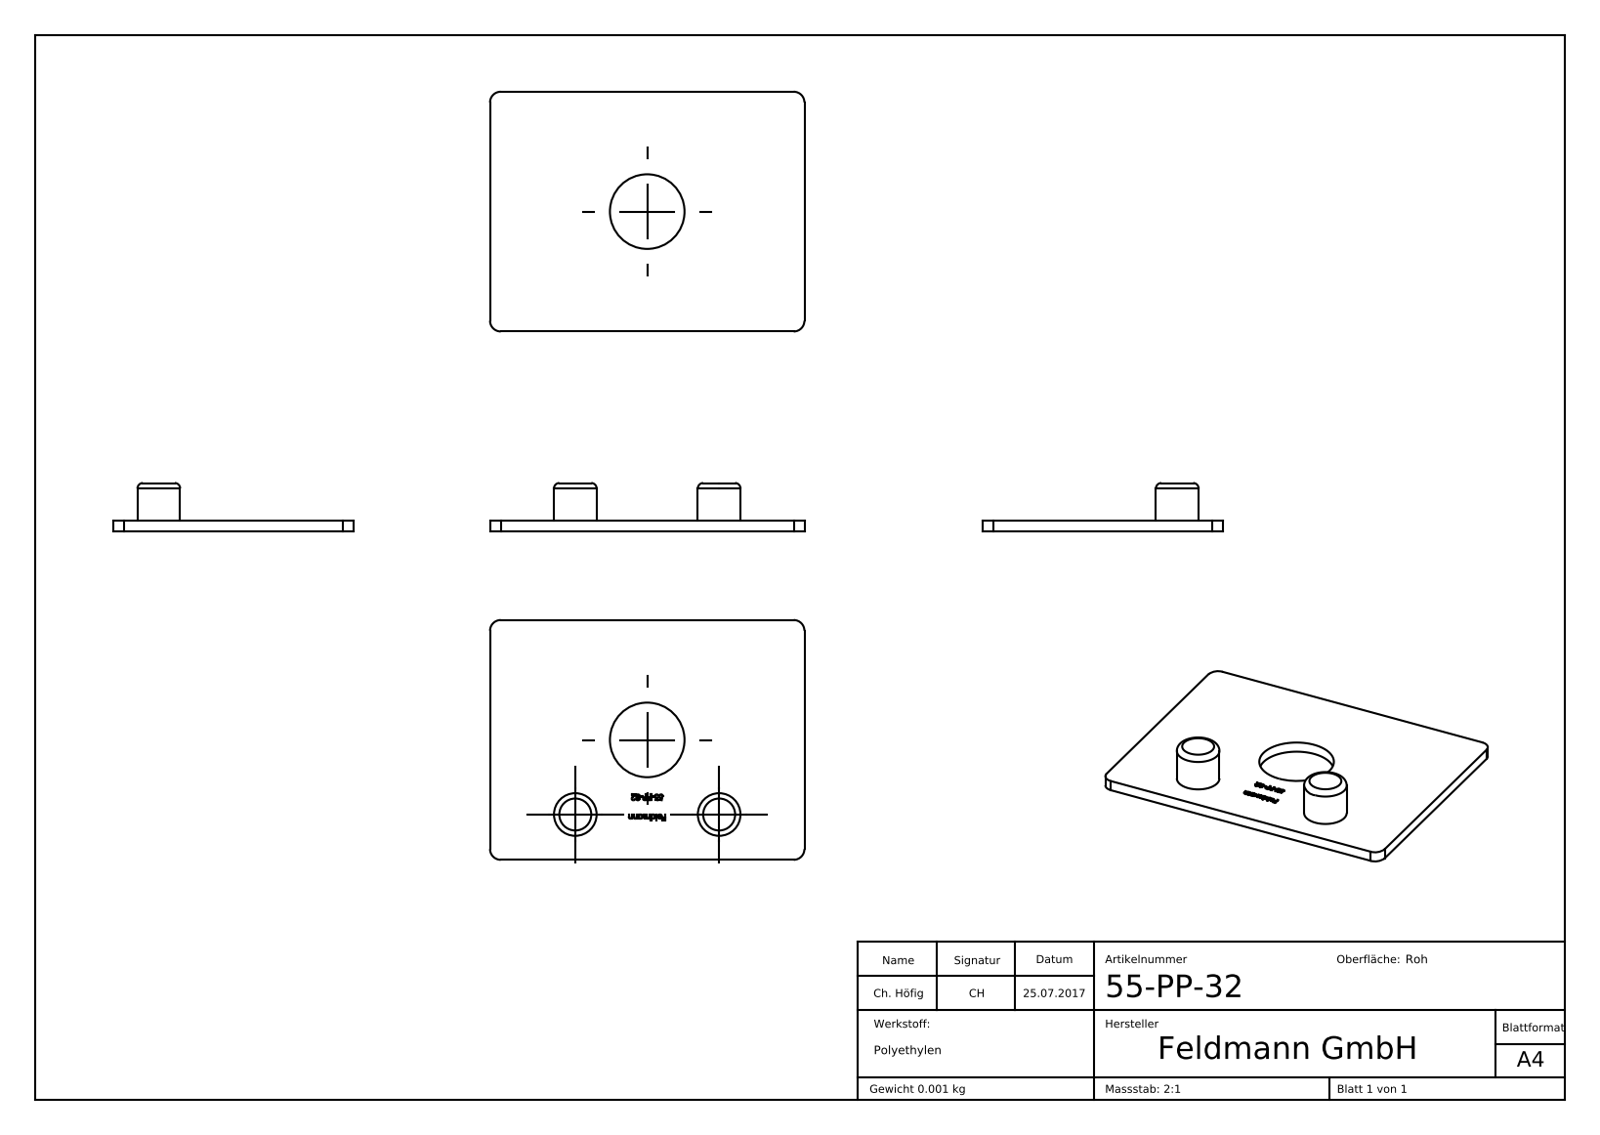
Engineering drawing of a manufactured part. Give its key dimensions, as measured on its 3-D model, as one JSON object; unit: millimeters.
{"part_name": "55-PP-32", "step_written_by": "SolidWorks 2015 (CONFIG_CONTROL_DESIGN)", "units": "millimeters", "bodies": {"solids": 1, "faces": 238, "planar": 128, "cylindrical": 10, "other": 100}, "overall_size": [29.5, 22.5, 4.5], "volume_mm3": 711, "surface_area_mm2": 1459, "round_holes": [[7, 1]], "round_bosses_or_shafts": [[4, 2]], "partial_cylinders_radius": [[1, 4]], "face_to_face_distances": [1, 22.5, 29.5, 4.5, 3.5, 0.9, 3.6, 1.35, 1.31, 1.19]}
